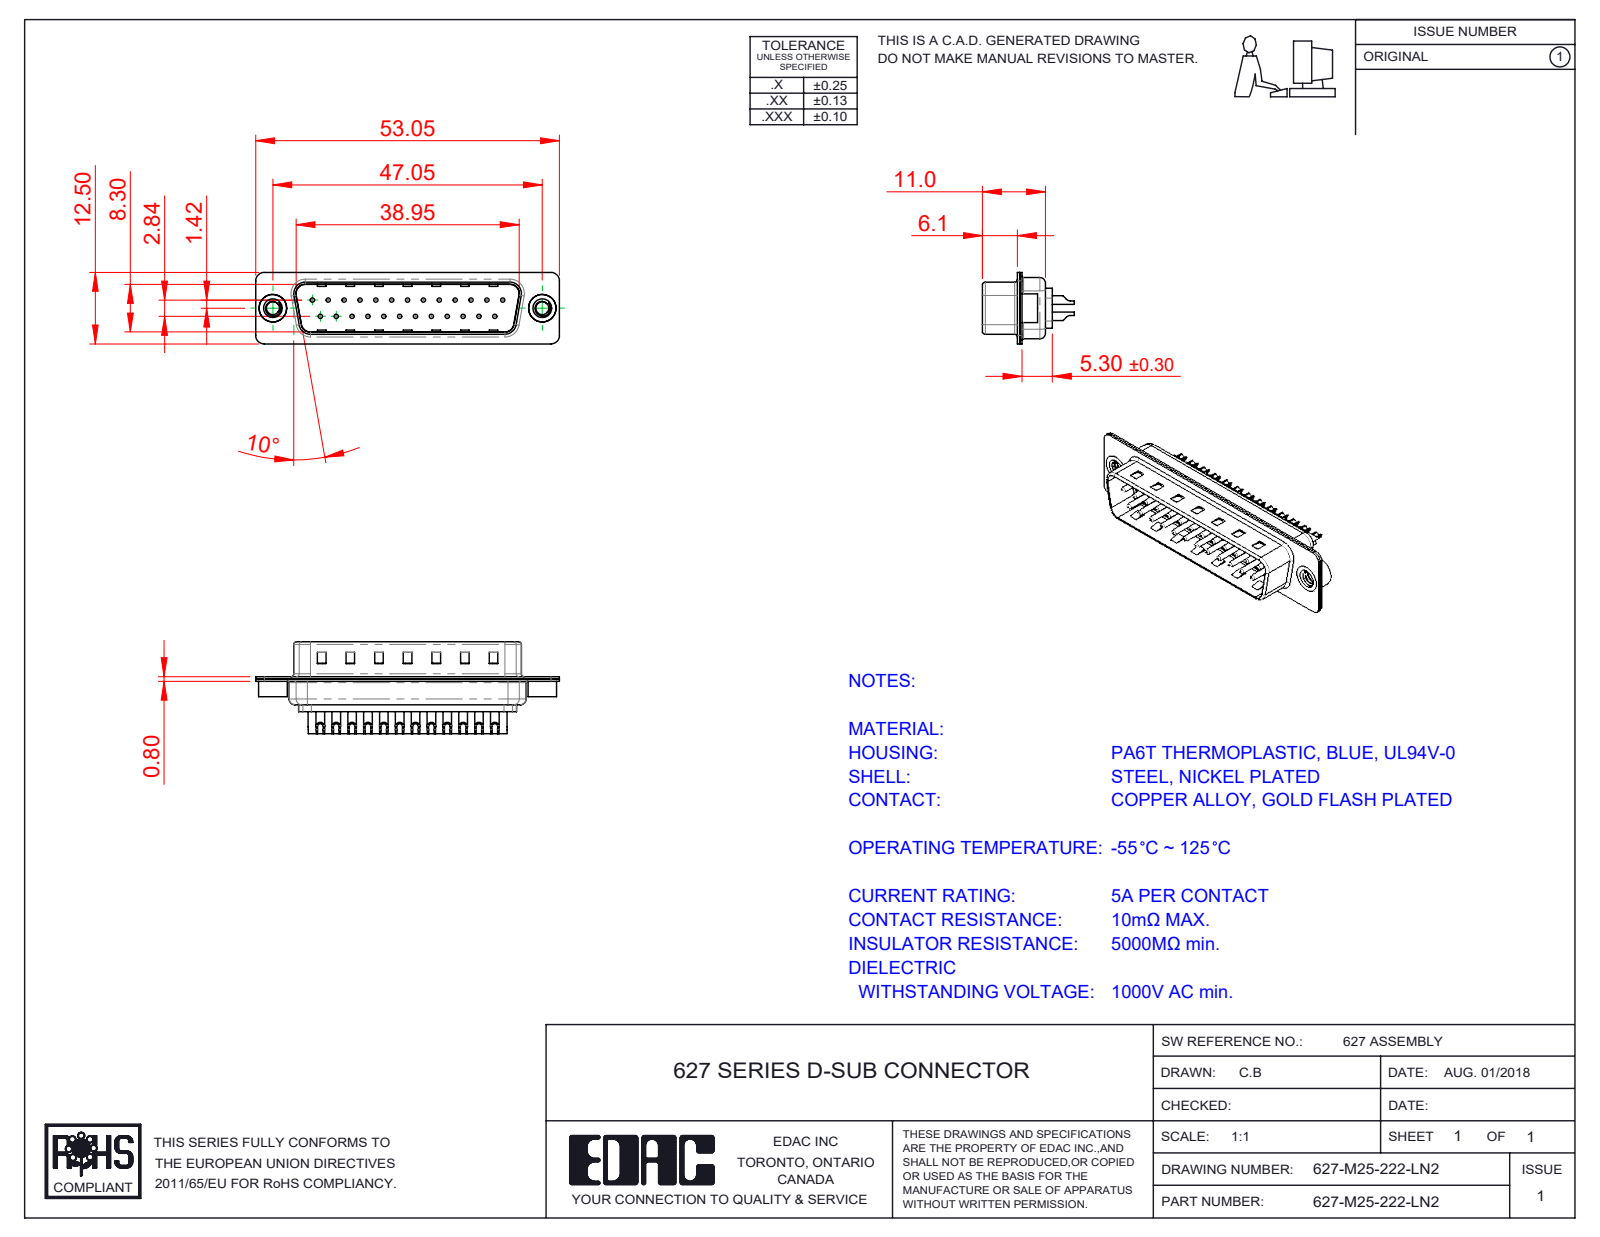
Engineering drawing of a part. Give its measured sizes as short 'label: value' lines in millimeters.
name: 627M Housing_25 Contacts; 627M Shell Front_25 Contacts; 627M Contact Row 2_22; 627M Shell Rear_25 Contacts (+3 more)
written by: SolidWorks 2020 (CONFIG_CONTROL_DESIGN)
unit: mm
bodies: 30 solids, 1301 faces (396 planar, 537 cylindrical, 368 other)
size: 53.05 × 16.05 × 12.5
volume: 2 776 mm³; area: 7 078 mm²
holes: 25× ⌀0.75, 25× ⌀1, 25× ⌀1.6, 25× ⌀2, 2× ⌀2.26, 2× ⌀4, 2× ⌀4.8
bosses: 25× ⌀1.5, 2× ⌀5, 2× ⌀4.9
rounds: 16× R1.5, 12× R2, 8× R0.5, 8× R1.6, 6× R1, 4× R0.25, 4× R0.6, 4× R0.65
face distances: 0.4, 0.8, 9.5, 9.1, 8.7, 9.9, 1.2, 0.75, 0.35, 6.1
hole spacings: 3.16, 2.77, 5.54, 8.31, 11.08, 13.85, 16.62, 5.03
